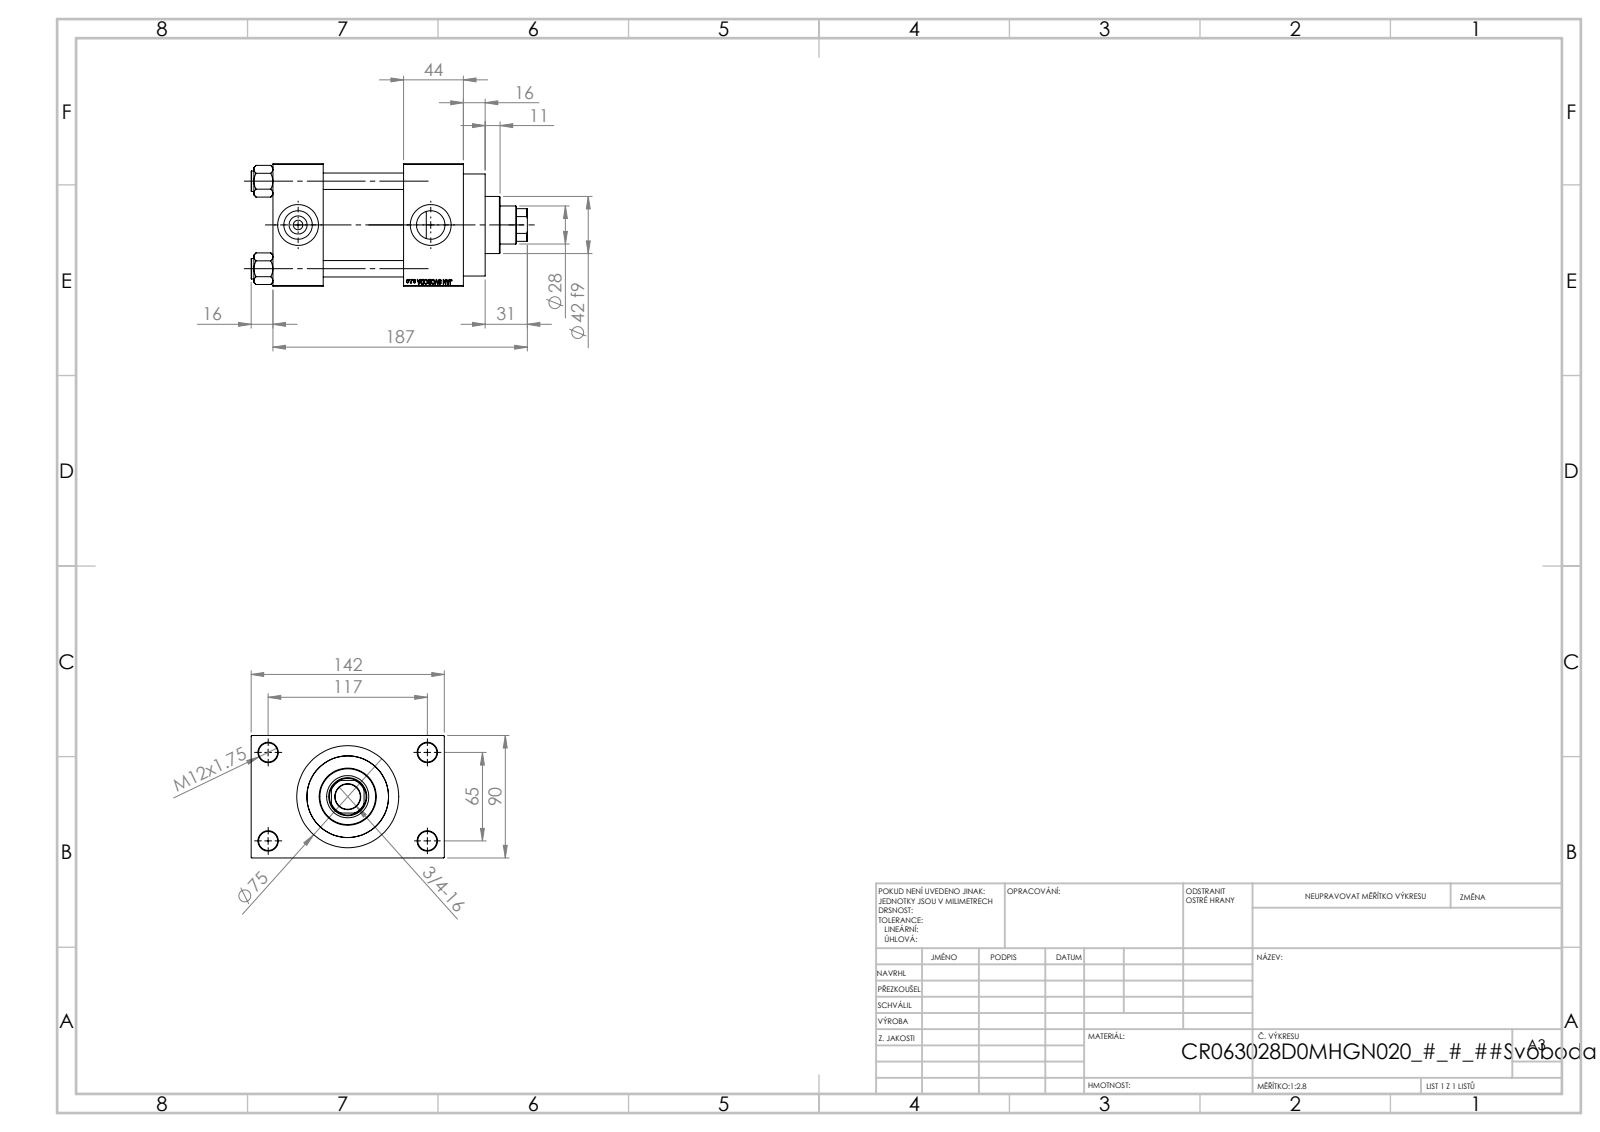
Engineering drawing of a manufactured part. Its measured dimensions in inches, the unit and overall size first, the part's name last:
Units: inches
Overall size (bounding box): 7.992 × 5.591 × 3.543
Round holes (diameter × count): ⌀0.472 ×4, ⌀0.551 ×4, ⌀0.276 ×2, ⌀0.825 ×2, ⌀1.181 ×2, ⌀0.728 ×1, ⌀1.102 ×1, ⌀1.22 ×1, ⌀1.969 ×1, ⌀2.362 ×1, ⌀2.48 ×1
Round bosses / shafts (diameter × count): ⌀0.591 ×4, ⌀2.953 ×1, ⌀2.717 ×1, ⌀1.654 ×1
Partial cylindrical surfaces — rounded edges, fillets, slot ends (radius × count): R0.531 ×1
Main face-to-face distances: 3.543, 2.323, 1.457, 3.78, 5.512, 4.055, 1.732, 1.024, 4.567, 0.63
Hole centre spacings: 1.037, 1.79, 2.531, 2.635, 2.748, 3.569, 4.383, 2.559
Volume: 66.88 in³ · Surface area: 310.5 in²
Bodies: 11 solids, 1103 faces (497 planar, 88 cylindrical, 518 other)
Part name (STEP PRODUCT): V215CR_D_Body; V215_VC_A; V215CR_D_TYCINKA; NUT_M5_D (+1 more)
STEP written by: SolidWorks 2019 (CONFIG_CONTROL_DESIGN)
